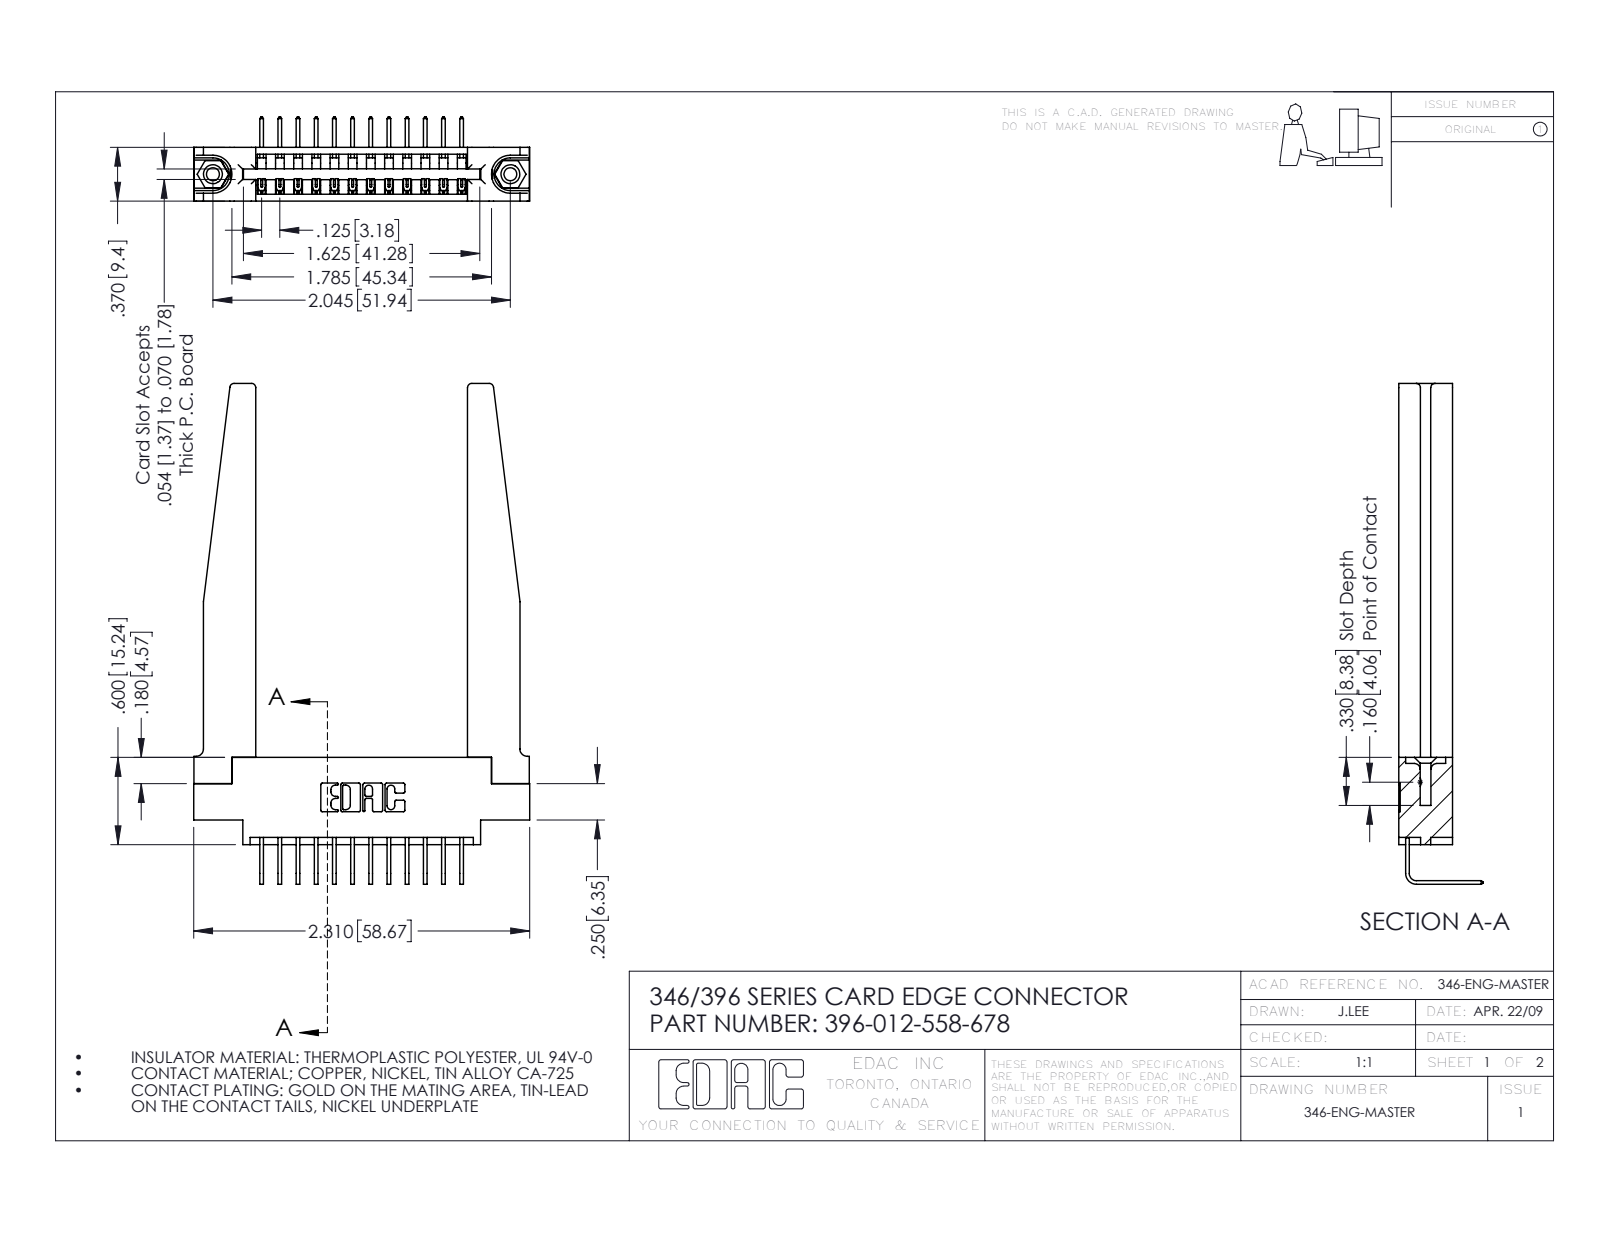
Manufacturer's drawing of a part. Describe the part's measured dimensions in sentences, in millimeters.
The part is named "346-220-078_345-220-078; 345-292-001_558 Tail - 2; 345-250-001_345-250-001-102; 396-012-558-678 (+1 more)". Its 3-D file was written by "SolidWorks 2016 (CONFIG_CONTROL_DESIGN)". It is 17 solids with 1080 faces: 726 planar, 302 cylindrical and 52 other. Overall it measures 87.5 by 58.7 by 14.7 millimeters. Its volume is 12 200 cubic millimeters and its surface area 13 230 square millimeters. Round holes: 2 of diameter 2.3, 2 of diameter 3.2, 2 of diameter 4, 1 of diameter 1.6. Round bosses or shafts: 2 of diameter 3.9. Partial cylindrical surfaces (rounded edges, fillets, slot ends): 24 of radius 0.2, 22 of radius 0.3, 8 of radius 0.8, 6 of radius 0.2, 6 of radius 0.8, 3 of radius 0.7, 3 of radius 1.3, 2 of radius 0.8. The main face-to-face distances are 9.4, 3.8, 8.2, 1.8, 3.8, 1.2, 6.4, 5.6, 2.6, 4.4. The hole center spacings are 6.2, 46.7, 51.9.
